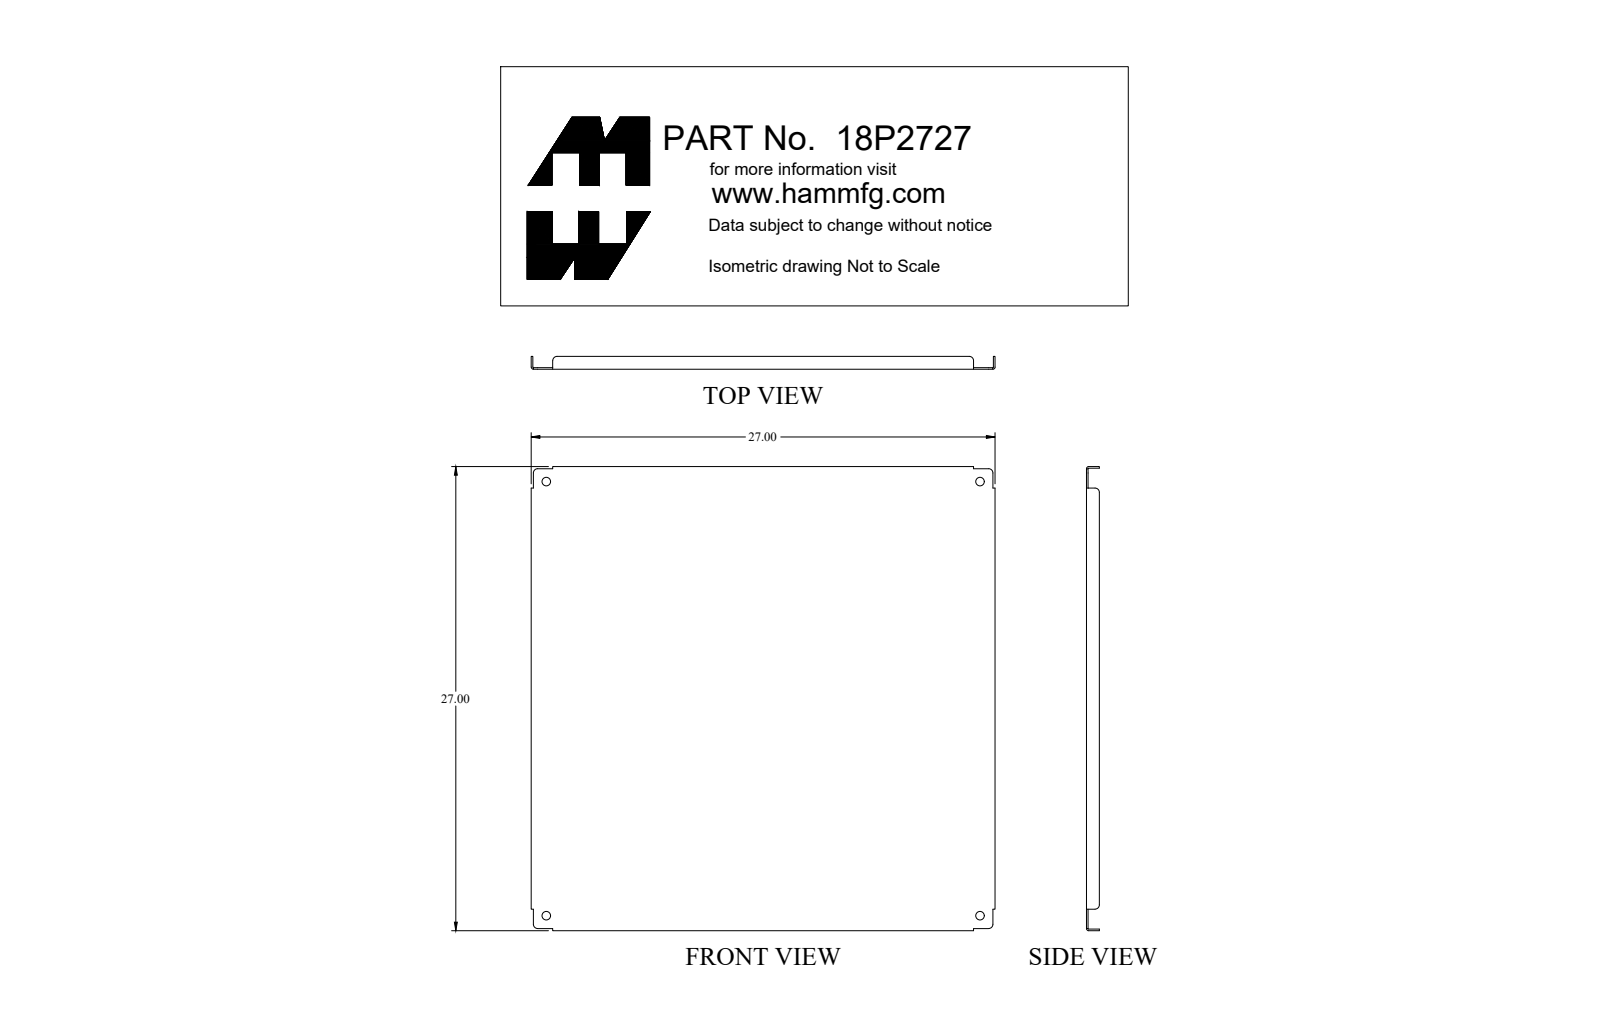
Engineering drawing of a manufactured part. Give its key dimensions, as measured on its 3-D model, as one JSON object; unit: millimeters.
{"part_name": "18P2727_Default", "step_written_by": "SolidWorks 2018 (CONFIG_CONTROL_DESIGN)", "units": "millimeters", "bodies": {"solids": 1, "faces": 58, "planar": 30, "cylindrical": 28, "other": 0}, "overall_size": [685.8, 685.8, 19.1], "volume_mm3": 1226000, "surface_area_mm2": 1024000, "round_holes": [[12.7, 4]], "partial_cylinders_radius": [[6.4, 8], [0.8, 4], [3.2, 4]], "face_to_face_distances": [2.4, 683.4, 681, 685.8, 19.1, 16.6, 3.2, 682.6, 0.8, 680.2], "hole_center_spacings": [641.4, 907]}
